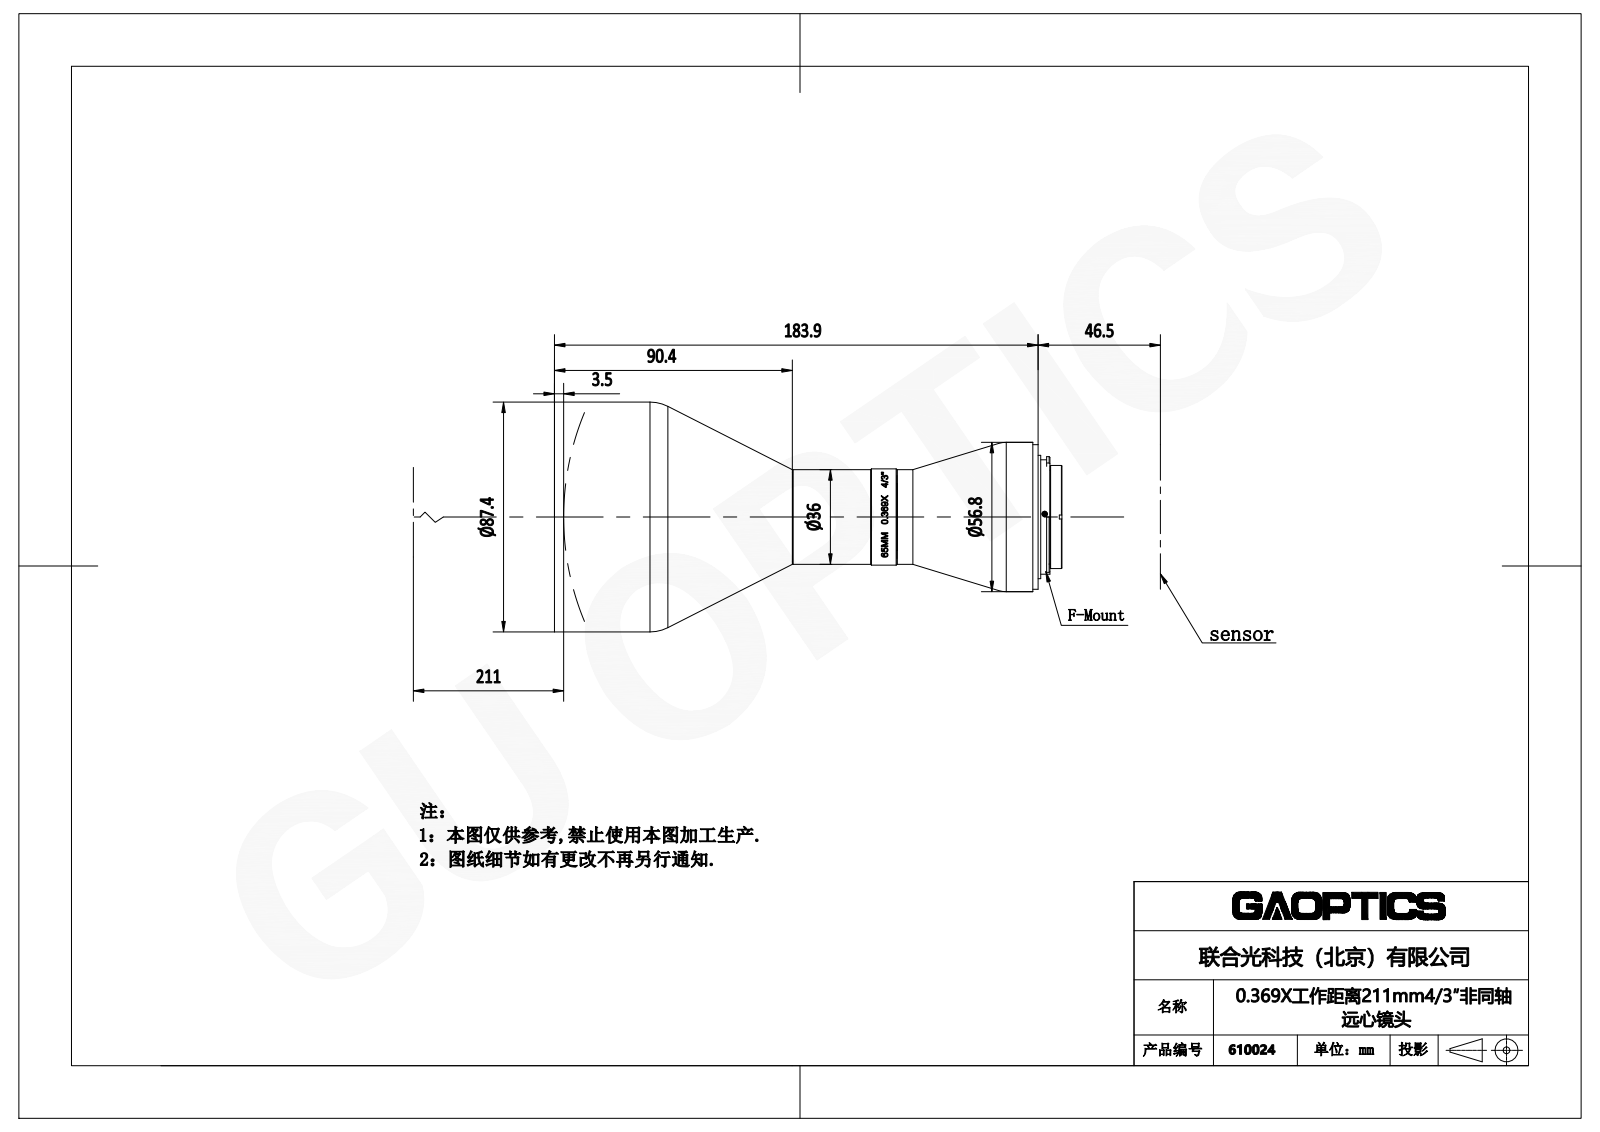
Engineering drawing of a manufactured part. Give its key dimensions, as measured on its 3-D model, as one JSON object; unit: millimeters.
{"part_name": "610024", "step_written_by": "SolidWorks 2020 (CONFIG_CONTROL_DESIGN)", "units": "millimeters", "bodies": {"solids": 0, "faces": 222, "planar": 74, "cylindrical": 69, "other": 79}, "overall_size": [192.8, 87.4, 87.4], "round_holes": [[2.2, 3], [3, 3], [1.4, 1], [29.4, 1], [35, 1], [36, 1], [40.3, 1], [56.8, 1], [87.4, 1]], "round_bosses_or_shafts": [[2.8, 2], [2, 2], [80.4, 1], [80.35, 1], [55, 1], [46.9, 1], [43.5, 1], [39.2, 1]], "partial_cylinders_radius": [[0.5, 8], [0.75, 2], [1, 1], [15.8, 1], [22.95, 1]], "face_to_face_distances": [164.92, 11.57, 176.49, 180.14, 168.57, 3.65, 183.74, 172.17, 7.25, 3.6], "hole_center_spacings": [25.5, 44.17, 44.18]}
